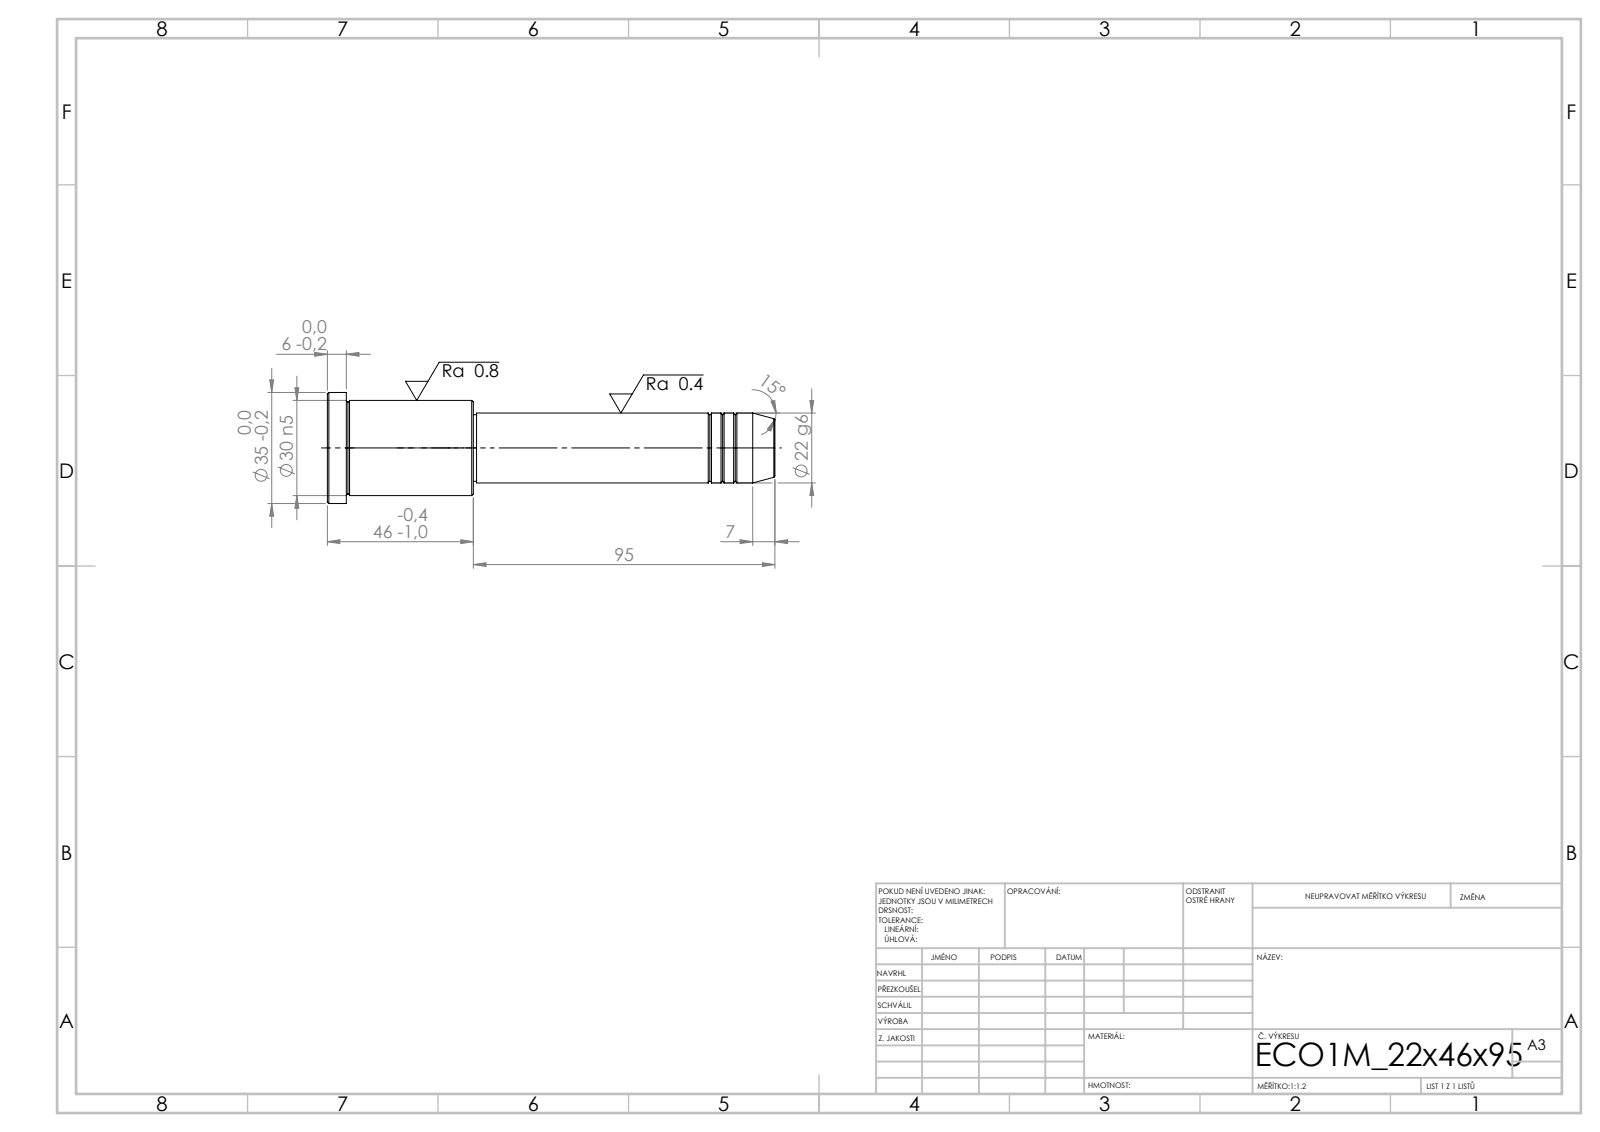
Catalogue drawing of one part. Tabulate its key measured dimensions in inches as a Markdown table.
| quantity | value |
| --- | --- |
| STEP written by | SolidWorks 2019 (CONFIG_CONTROL_DESIGN) |
| units | inches |
| bodies | 1 solid, 43 faces (5 planar, 14 cylindrical, 24 other) |
| overall size | 5.551 × 1.378 × 1.378 |
| volume | 4.245 in³ |
| surface area | 20.05 in² |
| round bosses / shafts (diameter × count) | 1.378 × 1, 1.181 × 1, 0.866 × 1, 0.827 × 1 |
| main face-to-face distances | 1.811, 1.575, 0.236, 3.74, 5.315, 5.551, 3.701, 0.039, 1.614, 1.85 |
